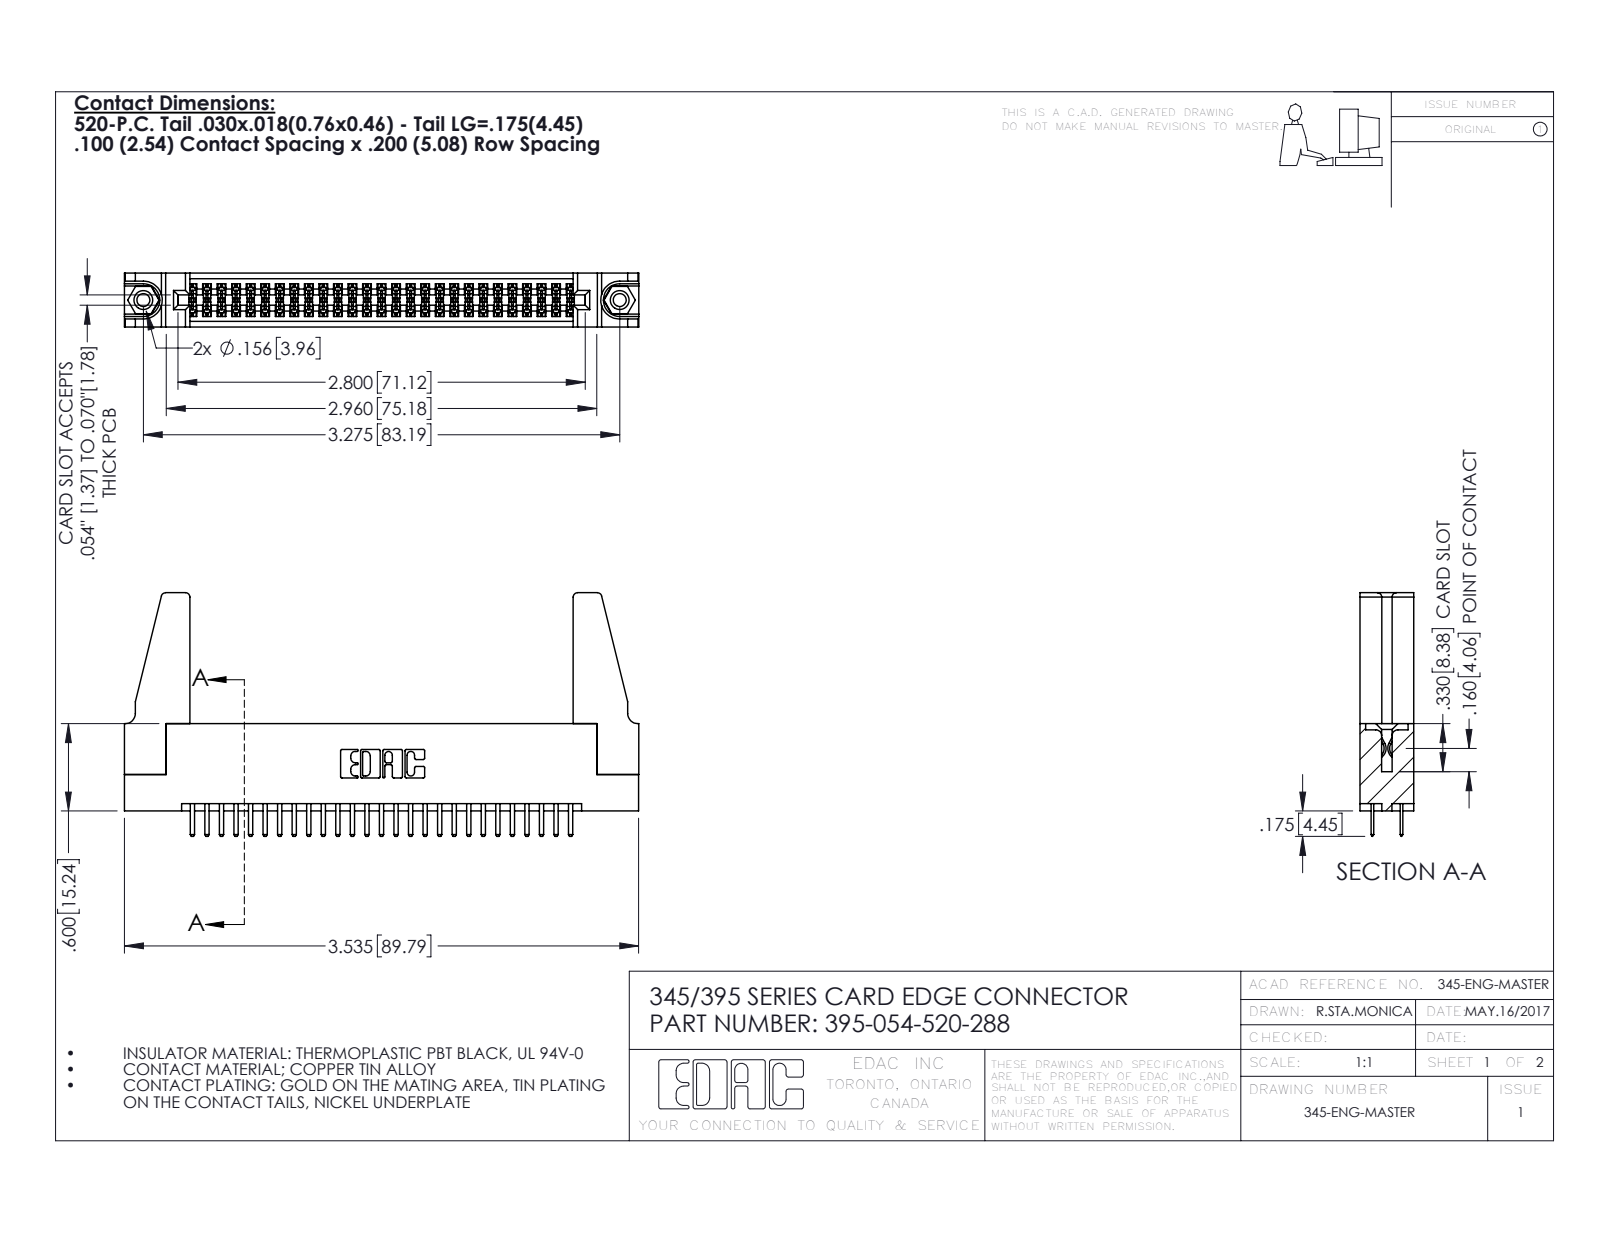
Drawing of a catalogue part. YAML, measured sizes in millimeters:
part_name: "345 Part_Flush Mounting Lugs - 0.156 Dia-TH; 345-292-001_345-293-120; 395-054-520-288; 345-250-001_345-250-001-102 (+1 more)"
step_written_by: "SolidWorks 2016 (CONFIG_CONTROL_DESIGN)"
units: millimeters
bodies: {solids: 59, faces: 3166, planar: 2042, cylindrical: 1108, other: 16}
overall_size: [89.8, 42.5, 9.4]
volume: 11800
surface_area: 15440
round_holes:
  - {diameter: 2.3, count: 2}
  - {diameter: 3.2, count: 2}
  - {diameter: 4, count: 2}
  - {diameter: 1.6, count: 1}
round_bosses_or_shafts:
  - {diameter: 3.9, count: 2}
partial_cylinders:
  - {radius: 0.2, count: 81}
  - {radius: 0.3, count: 58}
  - {radius: 0.3, count: 22}
  - {radius: 0.8, count: 8}
  - {radius: 0.2, count: 6}
  - {radius: 0.8, count: 6}
  - {radius: 0.7, count: 3}
  - {radius: 0.4, count: 2}
face_to_face_distances: [1.8, 9.4, 7.6, 5.1, 2.5, 6.9, 0.6, 5.7, 0.6, 1.8]
hole_center_spacings: [6.9, 77.2, 83.2]
